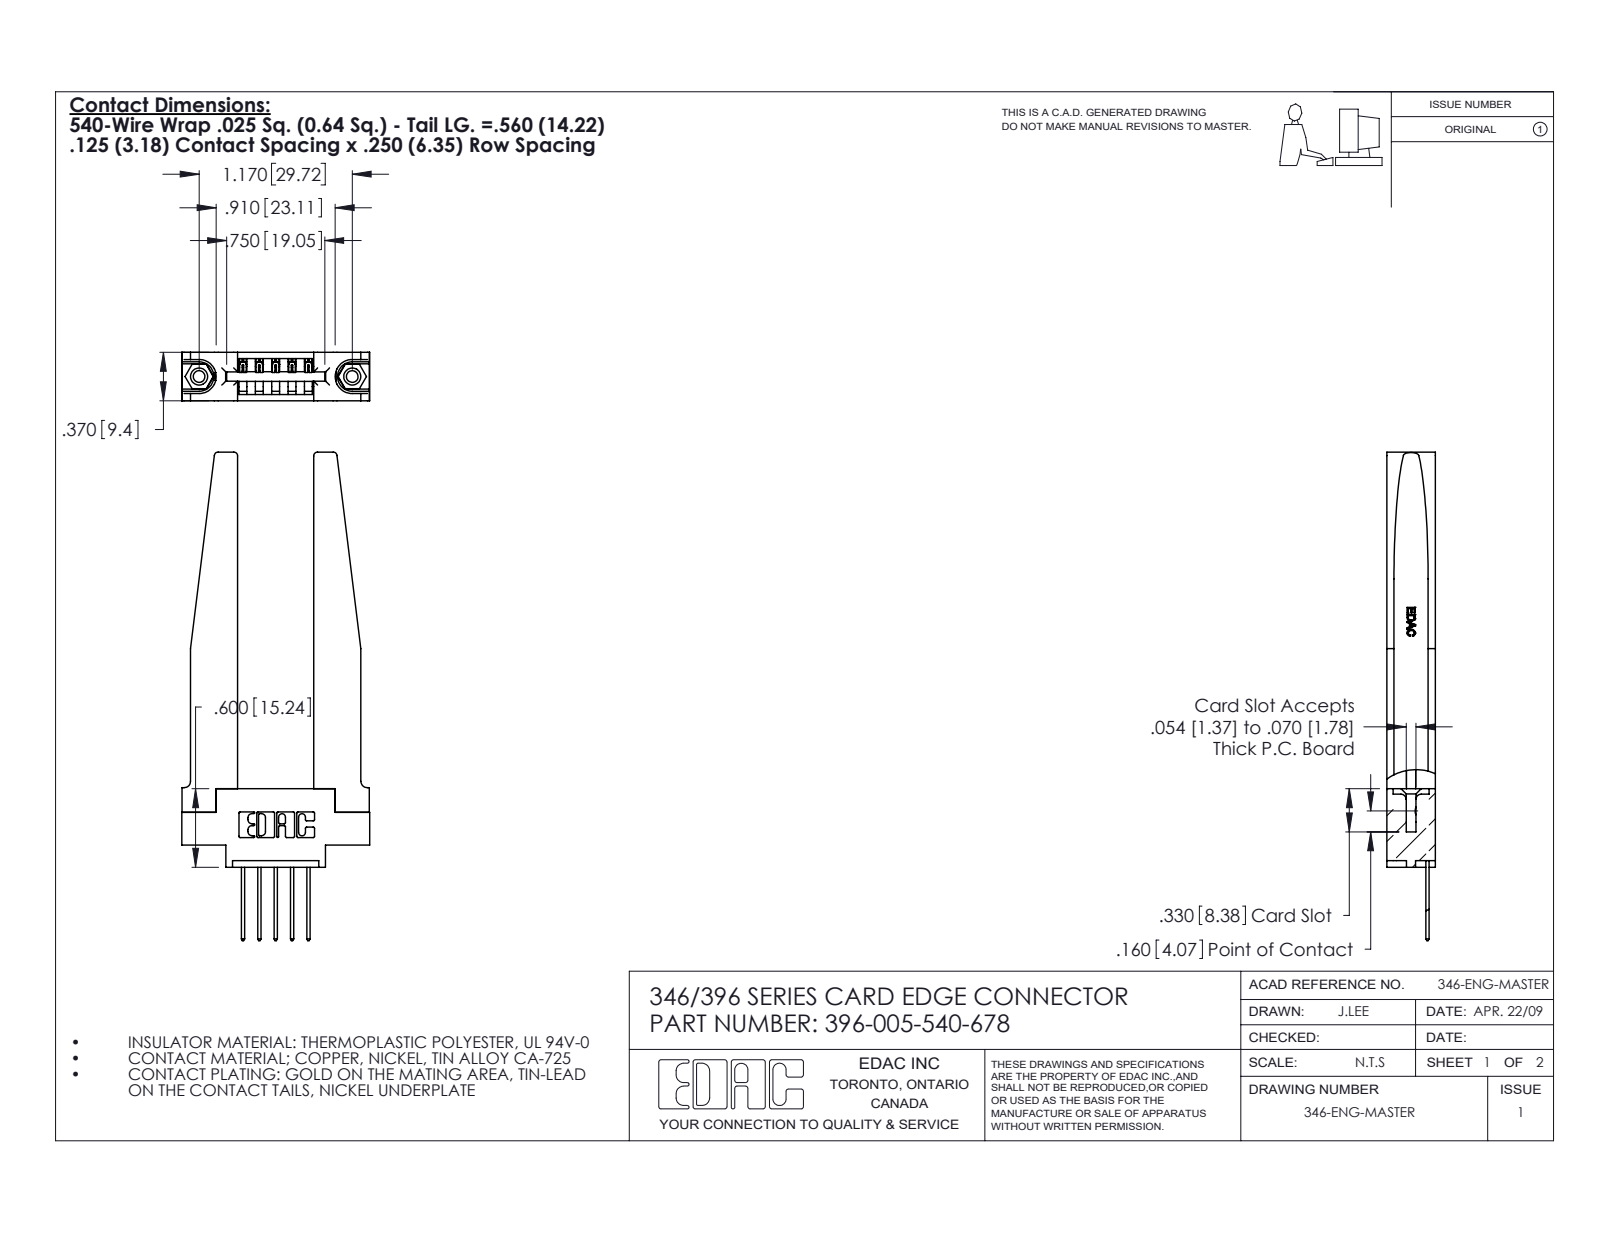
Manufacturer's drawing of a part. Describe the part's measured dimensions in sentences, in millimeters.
The part is named "346 Part_0.170 Offset - 0.156 Dia-TH; 345-250-001_345-250-001-102; 396-005-540-678; 346-220-078_345-220-078 (+1 more)". Its 3-D file was written by "SolidWorks 2020 (CONFIG_CONTROL_DESIGN)". It is 10 solids with 664 faces: 436 planar, 176 cylindrical and 52 other. Overall it measures 94.7 by 36.4 by 9.4 millimeters. Its volume is 9 980 cubic millimeters and its surface area 10 220 square millimeters. Round holes: 2 of diameter 2.3, 2 of diameter 3.2, 2 of diameter 4, 1 of diameter 1.6. Round bosses or shafts: 2 of diameter 3.9. Partial cylindrical surfaces (rounded edges, fillets, slot ends): 22 of radius 0.3, 10 of radius 0.2, 10 of radius 0.3, 8 of radius 0.8, 6 of radius 0.2, 6 of radius 0.8, 3 of radius 0.7, 2 of radius 0.8. The main face-to-face distances are 9.4, 3.8, 5.6, 14.8, 6.4, 1.8, 3.8, 2.6, 1.2, 8.2. The hole center spacings are 6.2, 24.6, 29.7.
